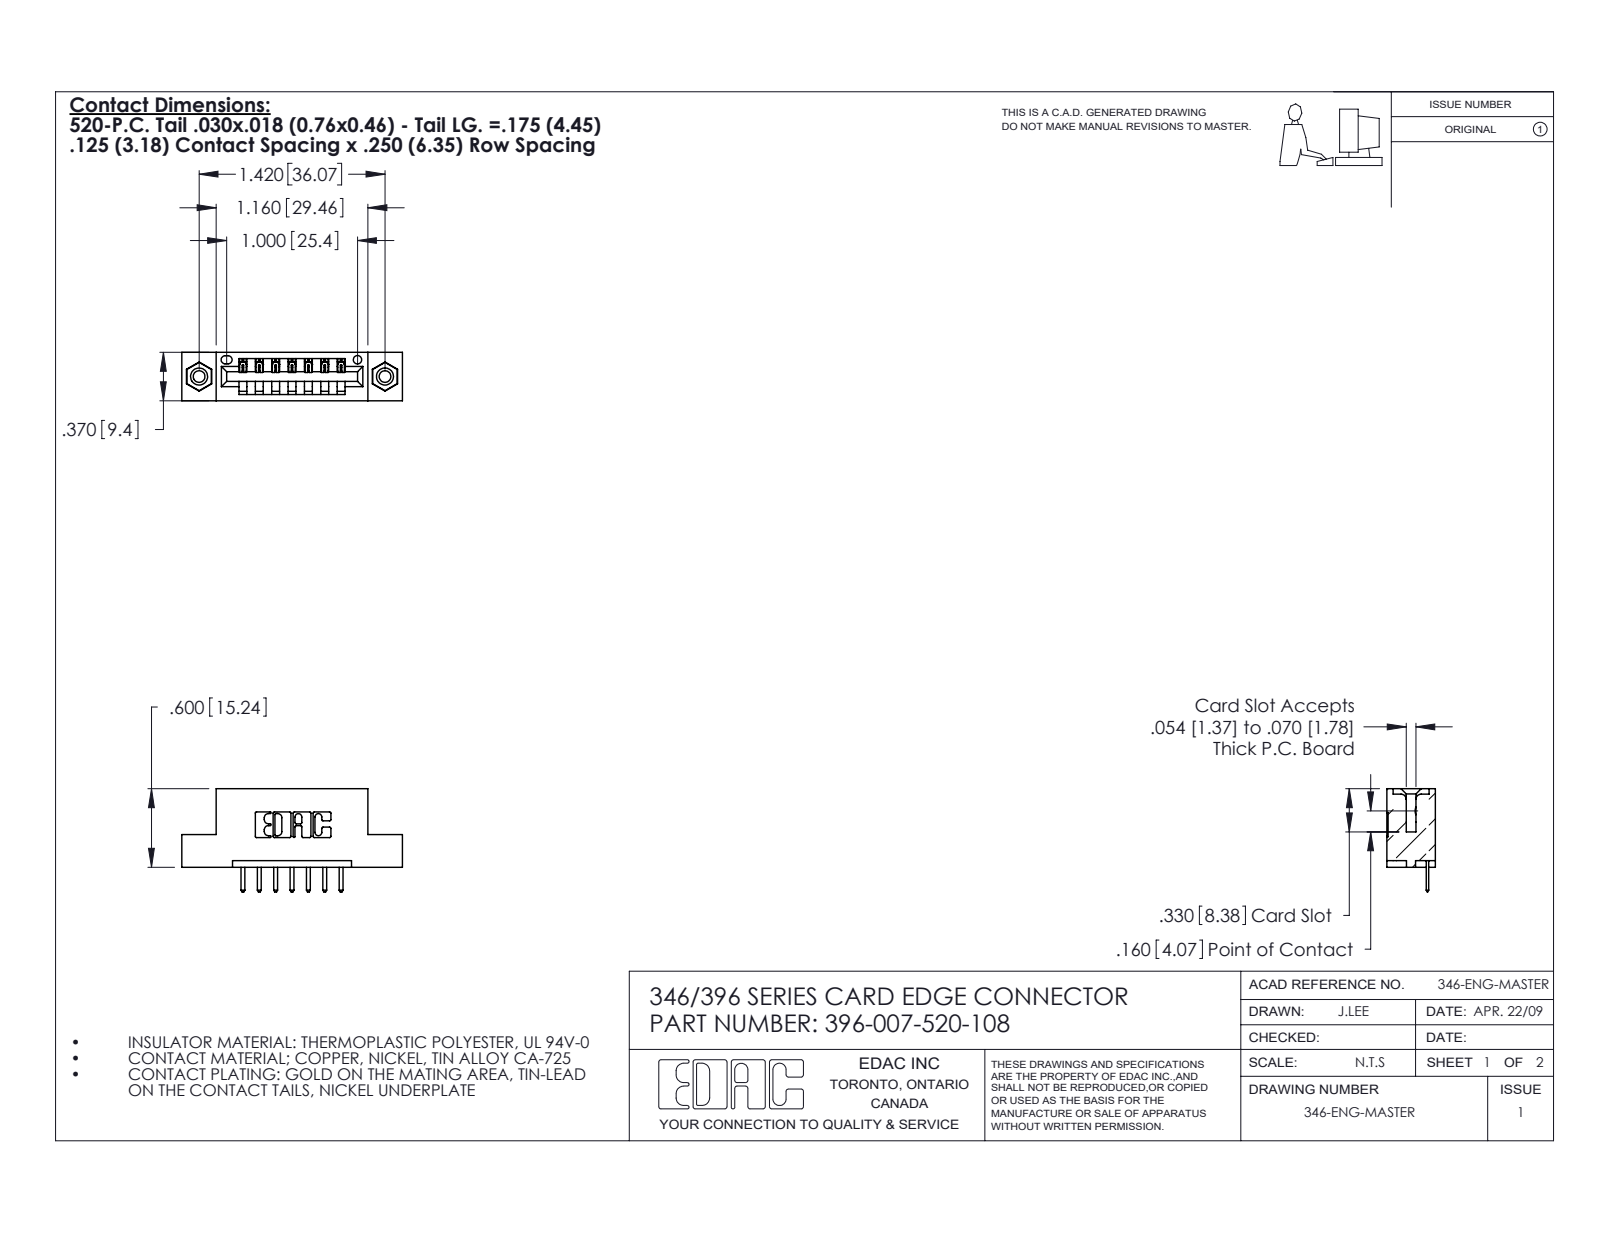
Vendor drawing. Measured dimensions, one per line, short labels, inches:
name: 396-007-520-108; 345-250-001_345-250-003-102; 346 Part_Flush Mounting Lugs - 0.156 Dia-TI; 345-292-001_345-293-120
written by: SolidWorks 2020 (CONFIG_CONTROL_DESIGN)
unit: in
bodies: 10 solids, 616 faces (402 planar, 198 cylindrical, 16 other)
size: 1.685 × 0.788 × 0.37
volume: 0.234 in³; area: 6.762 in²
holes: 2× ⌀0.089, 2× ⌀0.125, 2× ⌀0.156, 1× ⌀0.064
bosses: 2× ⌀0.155
rounds: 22× R0.01, 16× R0.01, 14× R0.006, 6× R0.007, 6× R0.031, 3× R0.026, 2× R0.031, 2× R0.04
face distances: 0.25, 0.37, 0.048, 0.322, 0.148, 0.222, 0.1, 0.174, 0.125, 0.185
hole spacings: 0.246, 1.217, 1.42
